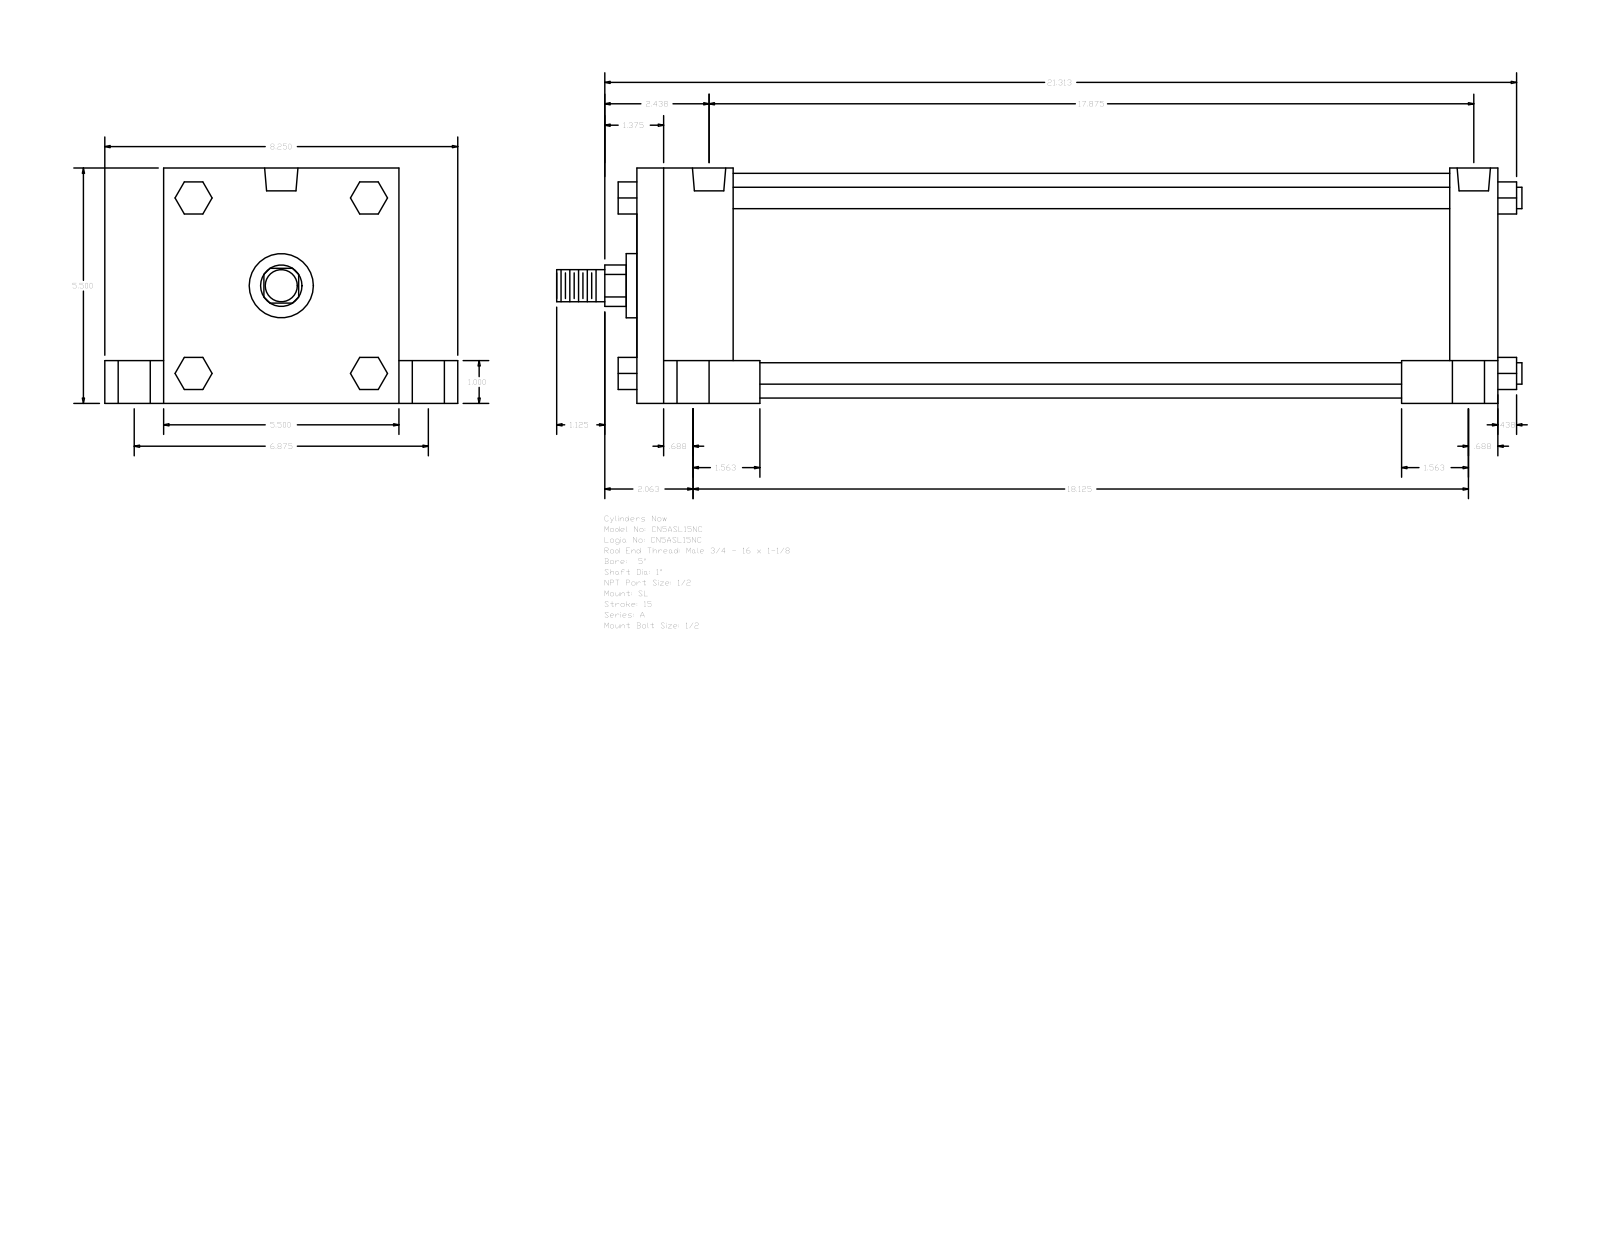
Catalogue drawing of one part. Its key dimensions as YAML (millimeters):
part_name: "A_SL__0500_1"
step_written_by: "GSSL Pune (CONFIG_CONTROL_DESIGN)"
units: millimeters
bodies: {solids: 0, faces: 150, planar: 114, cylindrical: 36, other: 0}
overall_size: [573.09, 209.55, 139.7]
round_holes:
  - {diameter: 8.73, count: 4}
  - {diameter: 19.05, count: 4}
  - {diameter: 25.4, count: 4}
  - {diameter: 19.77, count: 2}
round_bosses_or_shafts:
  - {diameter: 12.7, count: 4}
  - {diameter: 133.35, count: 1}
  - {diameter: 38.1, count: 1}
  - {diameter: 25.4, count: 1}
  - {diameter: 19.05, count: 1}
partial_cylinders:
  - {radius: 12.29, count: 1}
face_to_face_distances: [139.7, 511.18, 28.58, 25.4, 114.3, 34.93, 174.63, 57.15, 482.6, 425.45]
hole_center_spacings: [2.39, 87.31, 87.37, 87.83, 88.12, 174.62, 449.25, 451.64]
